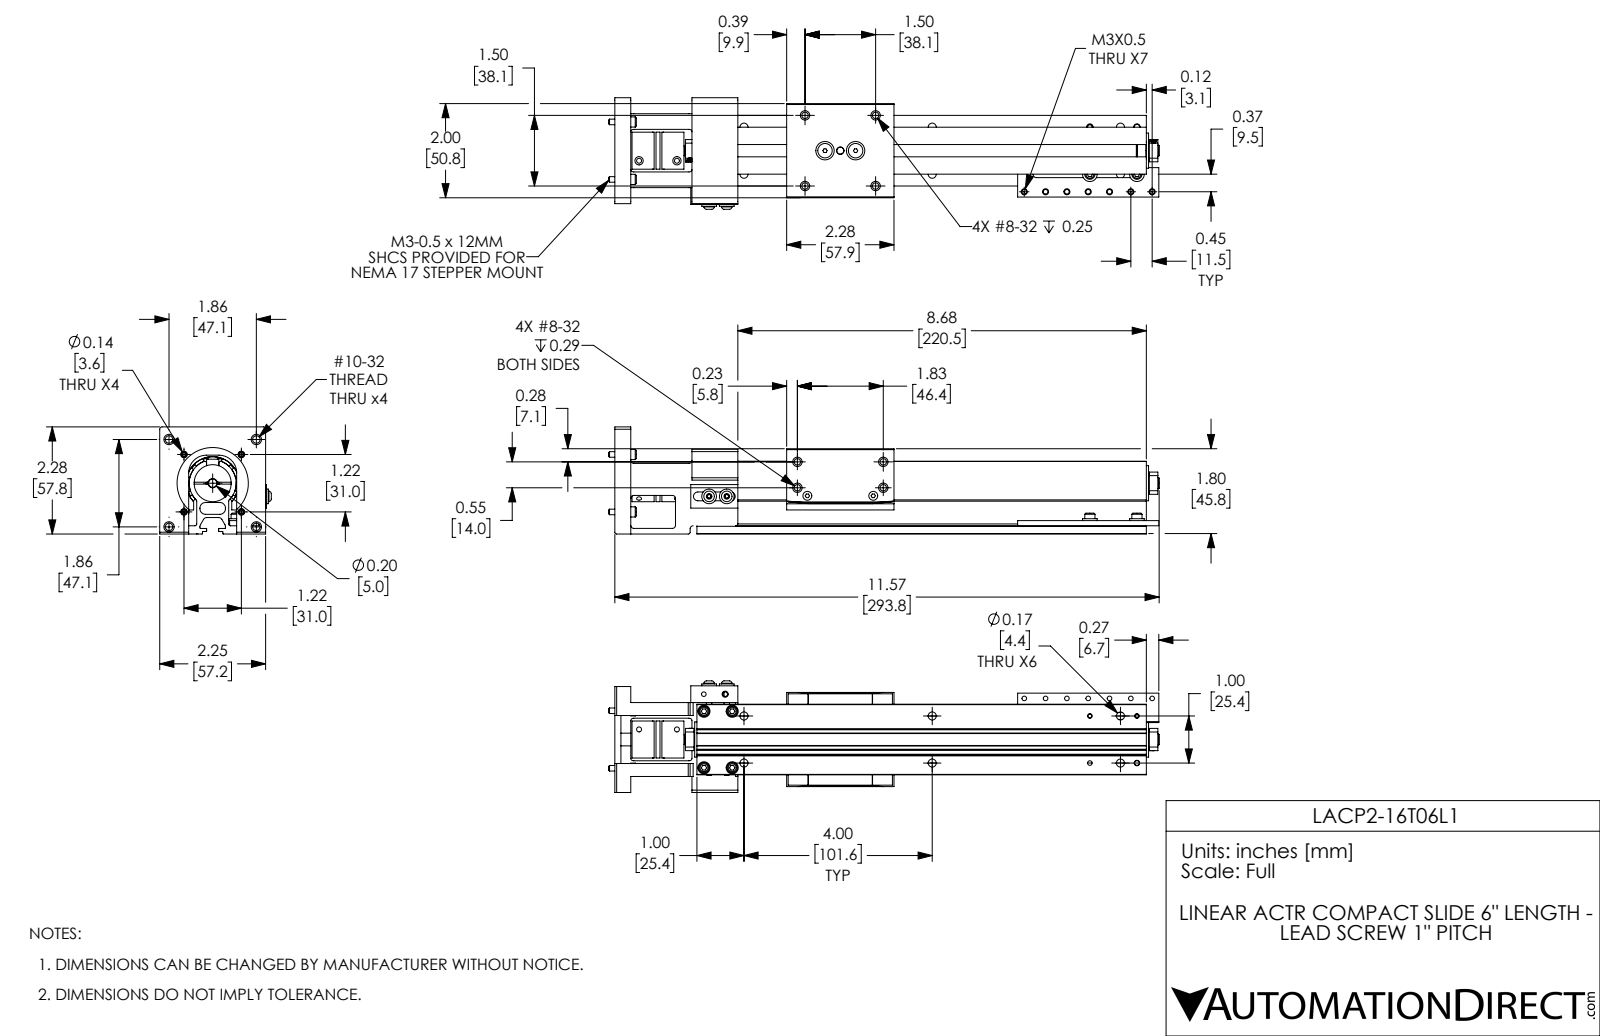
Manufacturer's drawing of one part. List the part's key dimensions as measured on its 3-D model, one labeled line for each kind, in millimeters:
Part name (STEP PRODUCT): LACP2-16T06L1; LACP2-16T06L1_BLOCK; LACP2-16T06L1_BODY
STEP written by: SolidWorks 2017 (AUTOMOTIVE_DESIGN)
Units: millimetres
Bodies: 46 solids, 1236 faces (502 planar, 465 cylindrical, 269 other)
Overall size (bounding box): 297.2 × 60.2 × 57.8
Volume: 242 900 mm³ · Surface area: 144 600 mm²
Round holes (diameter × count): ⌀2.5 ×18, ⌀3.5 ×10, ⌀4.4 ×6, ⌀3.6 ×4, ⌀3.7 ×4, ⌀4 ×4, ⌀6.5 ×4, ⌀2.5 ×2, ⌀2.7 ×2, ⌀3 ×2, ⌀3.2 ×2, ⌀3.2 ×2
Round bosses / shafts (diameter × count): ⌀5.5 ×10, ⌀3 ×10, ⌀7.9 ×4, ⌀3 ×3, ⌀7.8 ×2, ⌀5.7 ×2, ⌀4.2 ×2, ⌀3.5 ×2
Partial cylindrical surfaces — rounded edges, fillets, slot ends (radius × count): R0.3 ×17, R1.3 ×9, R1 ×8, R1.7 ×7, R0.5 ×4, R1.9 ×4, R2 ×4, R3 ×4
Main face-to-face distances: 4.4, 8.6, 12.4, 4.3, 21.6, 11.3, 28.5, 16.8, 34, 38.4
Hole centre spacings: 25.4, 11.5, 21.9, 23, 33.3, 39.9, 47.1, 11.5
